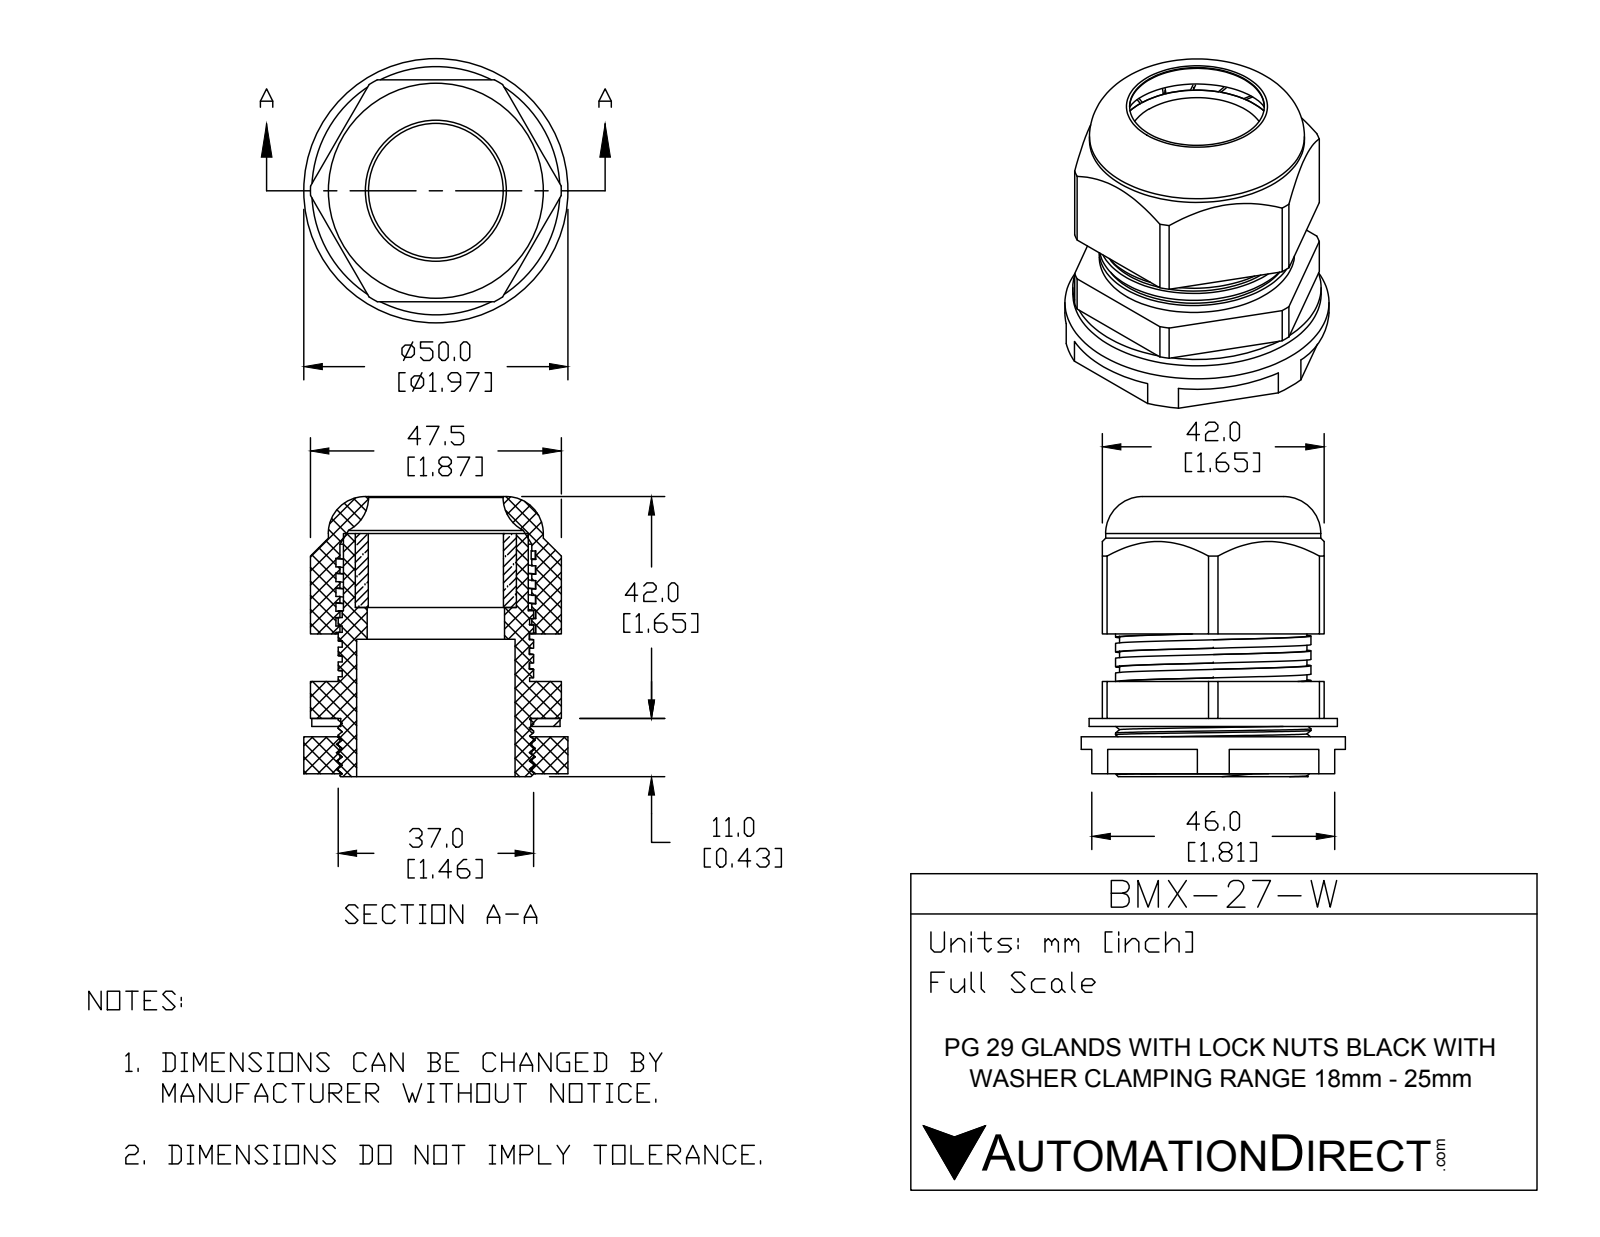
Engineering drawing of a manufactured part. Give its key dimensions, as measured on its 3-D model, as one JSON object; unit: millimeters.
{"part_name": "BMX-27-W", "step_written_by": "SolidWorks 2015 (CONFIG_CONTROL_DESIGN)", "units": "millimeters", "bodies": {"solids": 5, "faces": 219, "planar": 113, "cylindrical": 85, "other": 21}, "overall_size": [53, 50, 50], "volume_mm3": 39418, "surface_area_mm2": 31035, "round_holes": [[25.5, 1], [25.58, 1], [26, 1], [30, 1], [30.5, 1], [36, 1], [36.33, 1]], "round_bosses_or_shafts": [[50, 1], [47, 1], [40.7, 1], [37, 1], [35, 1]], "partial_cylinders_radius": [[23.75, 1]], "face_to_face_distances": [42, 9.5, 7, 1.5, 8, 2.5, 1, 14, 8.5, 16.5]}
